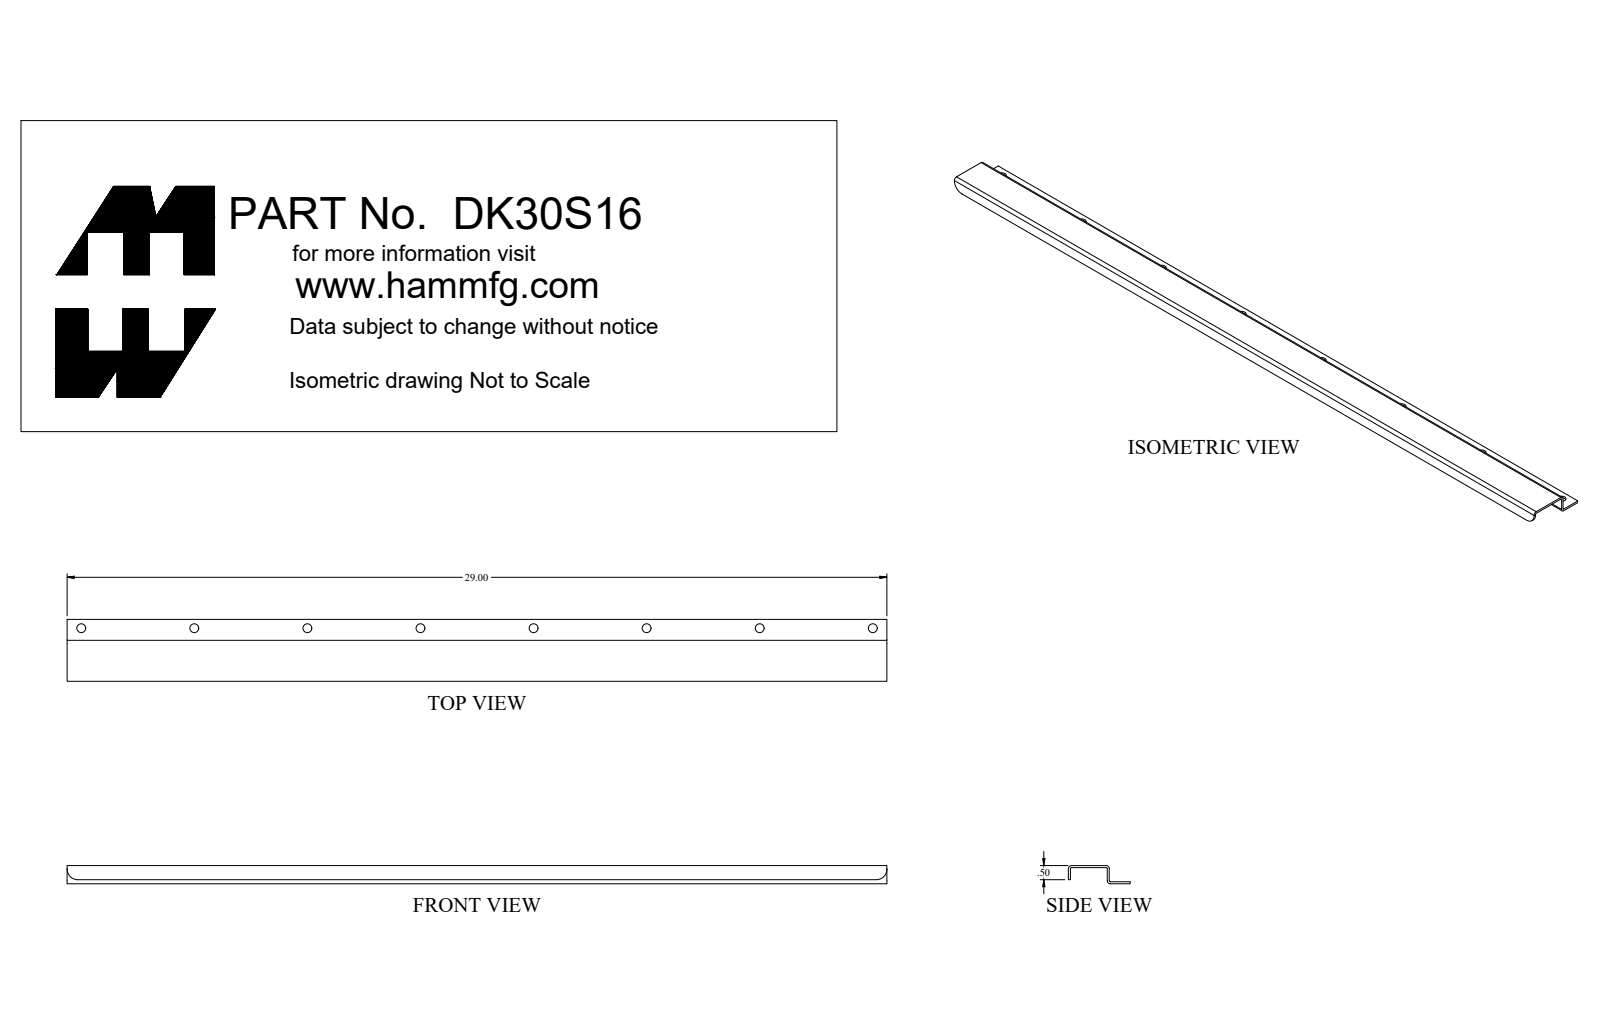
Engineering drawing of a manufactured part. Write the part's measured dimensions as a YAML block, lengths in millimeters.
part_name: "DK30S16_Default"
step_written_by: "SolidWorks 2018 (CONFIG_CONTROL_DESIGN)"
units: millimeters
bodies: {solids: 5, faces: 75, planar: 35, cylindrical: 34, other: 6}
overall_size: [736.6, 55.6, 33.6]
volume: 129400
surface_area: 150500
round_holes:
  - {diameter: 8, count: 8}
  - {diameter: 5.1, count: 1}
  - {diameter: 7, count: 1}
round_bosses_or_shafts:
  - {diameter: 15.9, count: 1}
  - {diameter: 12.3, count: 1}
  - {diameter: 6.4, count: 1}
partial_cylinders:
  - {radius: 0.9, count: 3}
  - {radius: 2.7, count: 3}
  - {radius: 9.5, count: 2}
face_to_face_distances: [1.8, 14.5, 16.4, 35, 12.7, 1.6, 16.1, 18, 3.4, 36.8]
hole_center_spacings: [101.6, 203.2, 304.8, 406.4, 508, 609.6, 711.2]
